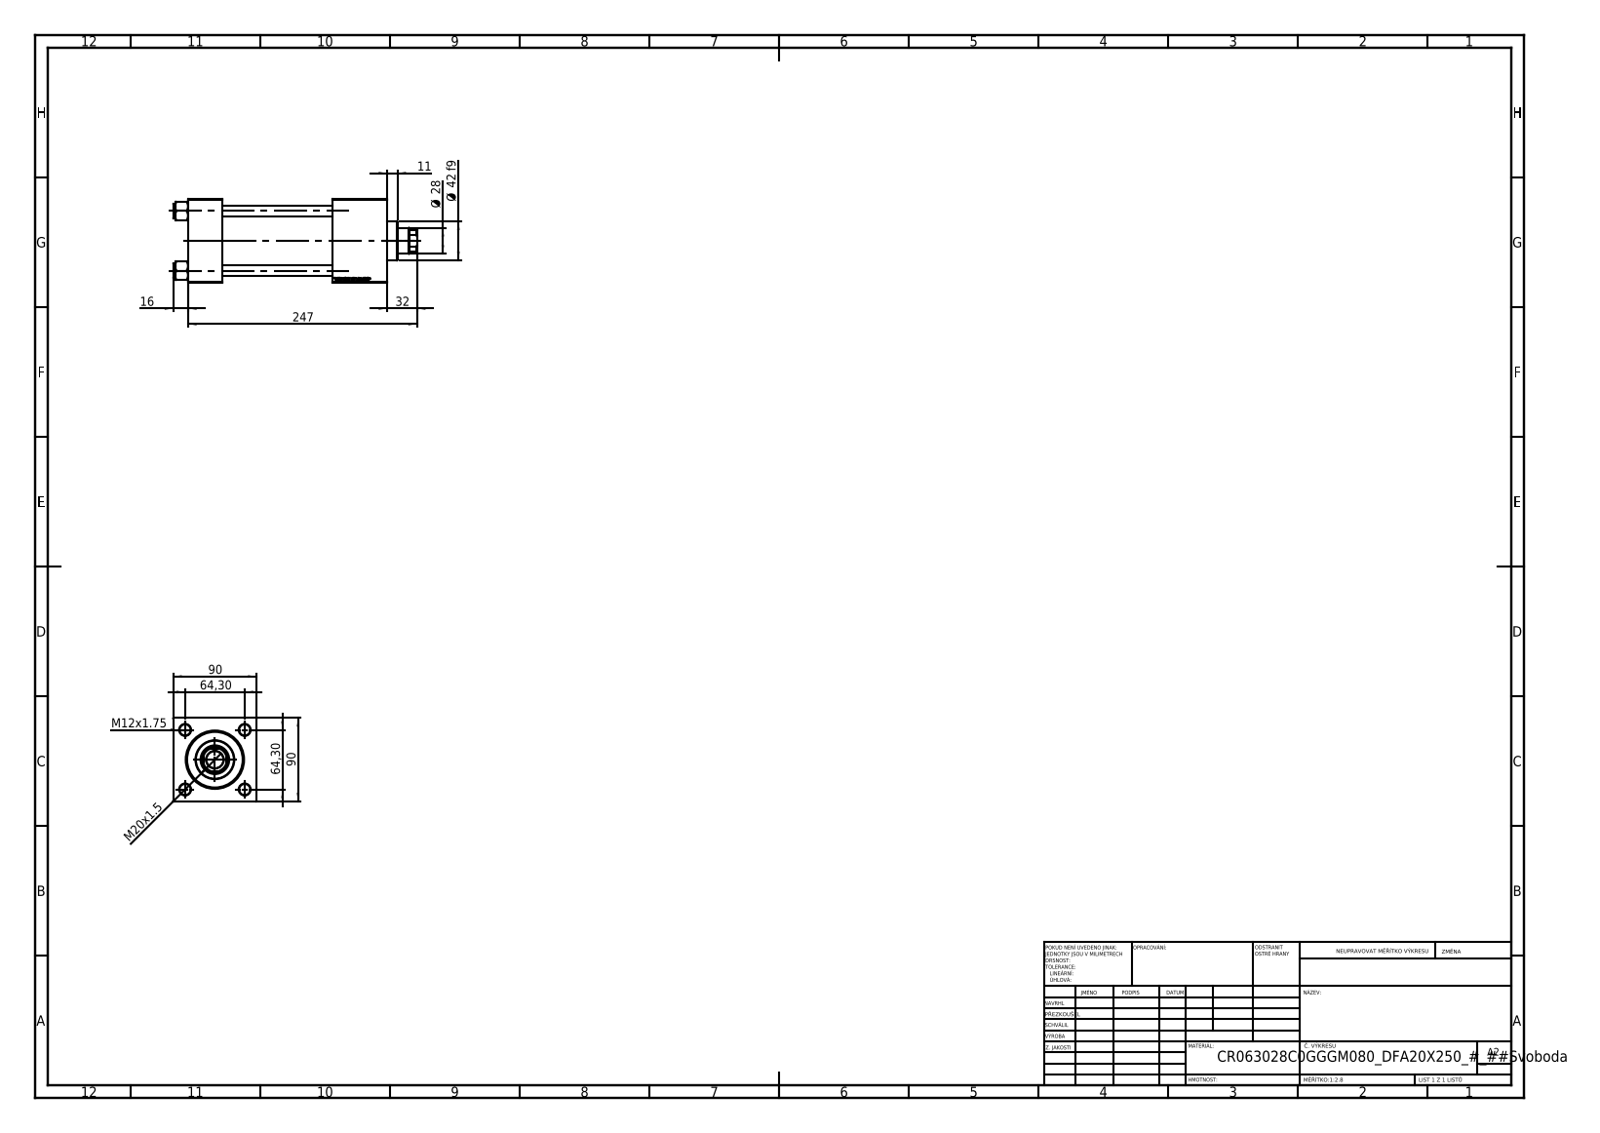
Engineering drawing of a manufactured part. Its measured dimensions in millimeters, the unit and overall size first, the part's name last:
Units: millimetres
Overall size (bounding box): 263 × 90 × 90
Round holes (diameter × count): ⌀12 ×4, ⌀7 ×2, ⌀20.96 ×2, ⌀30 ×2, ⌀18.5 ×1, ⌀28 ×1, ⌀31 ×1, ⌀50 ×1, ⌀60 ×1, ⌀63 ×1
Round bosses / shafts (diameter × count): ⌀15 ×4, ⌀69 ×1, ⌀42 ×1, ⌀36 ×1, ⌀30 ×1, ⌀20 ×1, ⌀18 ×1
Partial cylindrical surfaces — rounded edges, fillets, slot ends (radius × count): R7.5 ×1, R12 ×1, R13.5 ×1
Main face-to-face distances: 90, 37, 178, 215, 156, 119, 59, 186.3, 149.3, 30.3
Hole centre spacings: 45.47, 64.3, 90.93, 157.5
Volume: 1 072 000 mm³ · Surface area: 225 994 mm²
Bodies: 12 solids, 1182 faces (538 planar, 96 cylindrical, 548 other)
Part name (STEP PRODUCT): V215CR_C_Body; NUT_M5_C; FEMALE_PART_FOR_DFA; V215CR_VCP_C (+2 more)
STEP written by: SolidWorks 2019 (CONFIG_CONTROL_DESIGN)
